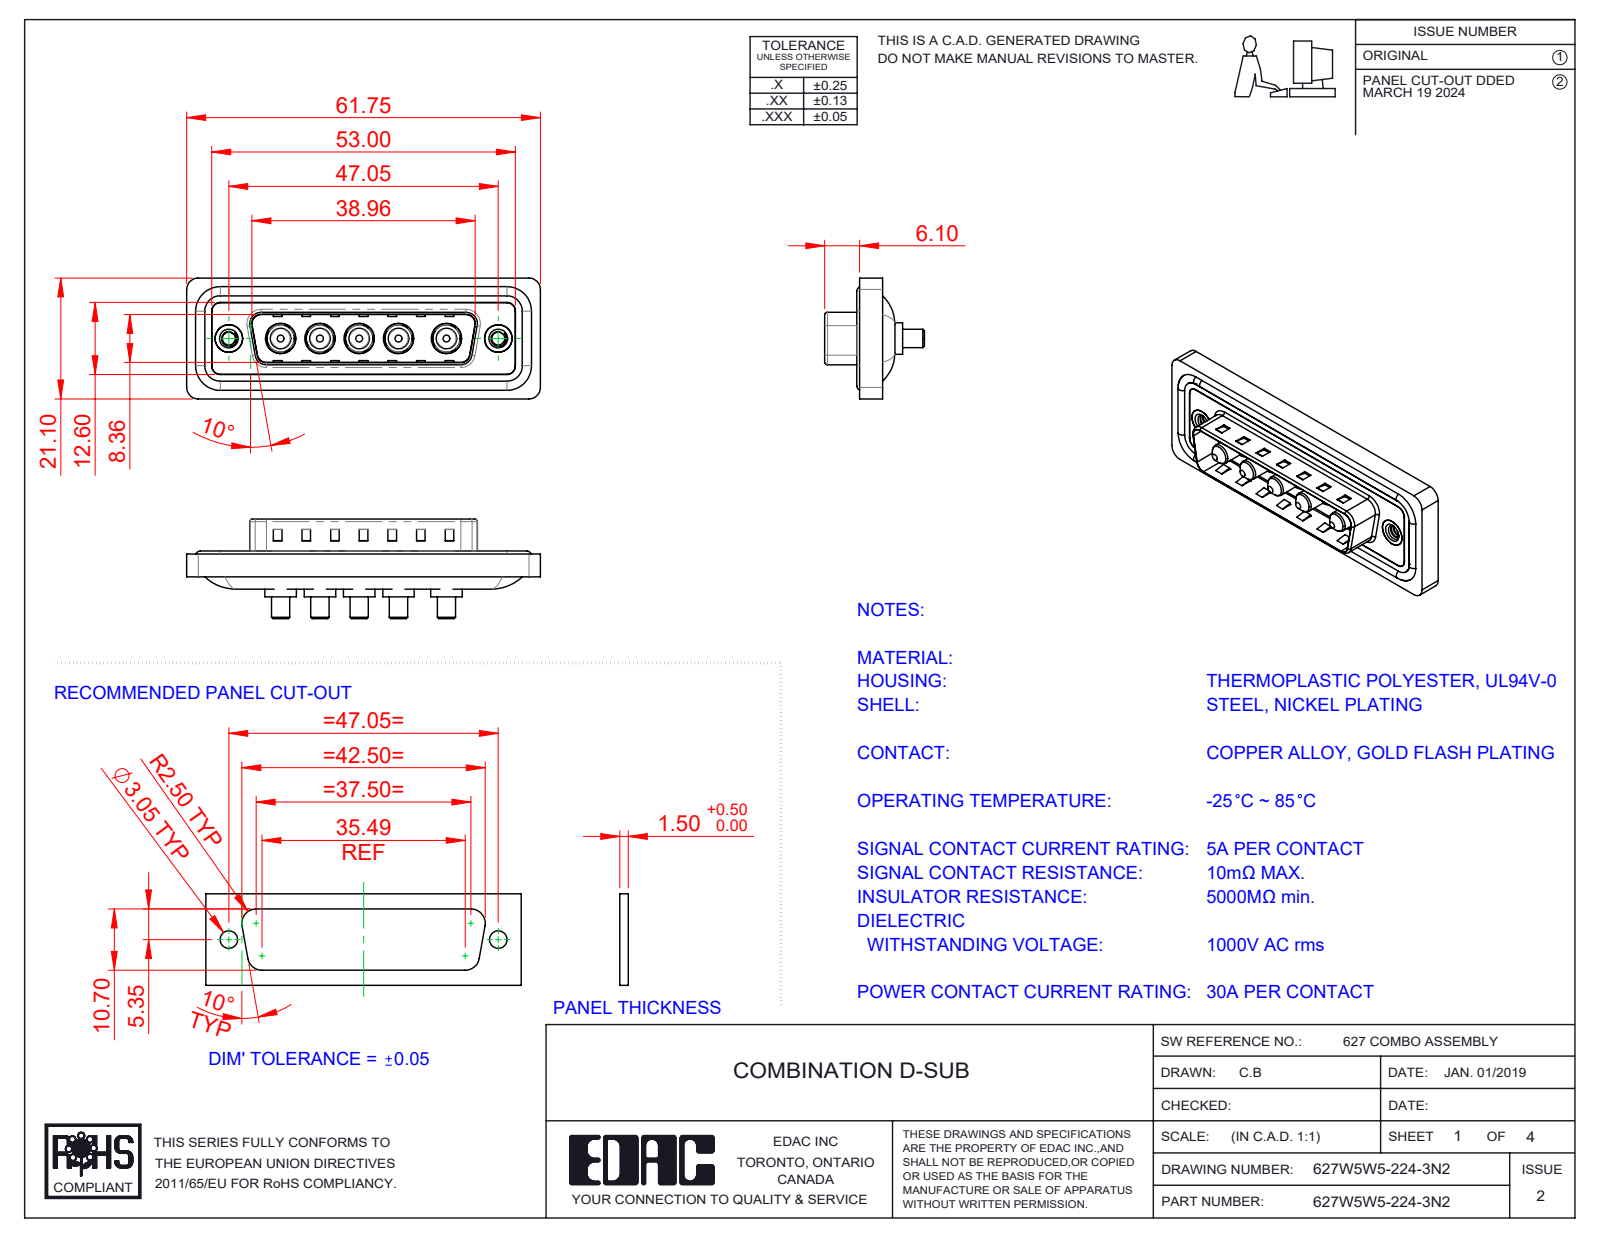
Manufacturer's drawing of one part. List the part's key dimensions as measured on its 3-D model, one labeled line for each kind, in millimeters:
Part name (STEP PRODUCT): 627Combo Waterproof Housing_25 Contacts; 627Combo Shell Rear_25 Contacts; 627Combo Threaded Rivet_2; 627Combo Housing_5W5 (+3 more)
STEP written by: SolidWorks 2023 (CONFIG_CONTROL_DESIGN)
Units: millimetres
Bodies: 17 solids, 678 faces (259 planar, 283 cylindrical, 136 other)
Overall size (bounding box): 61.75 × 21.1 × 17.4
Volume: 7 508 mm³ · Surface area: 11 819 mm²
Round holes (diameter × count): ⌀4.85 ×5, ⌀5.3 ×5, ⌀2.26 ×2, ⌀4 ×2, ⌀4.8 ×2, ⌀5 ×2
Round bosses / shafts (diameter × count): ⌀5.5 ×5, ⌀5.2 ×5, ⌀4.75 ×5, ⌀3.75 ×5, ⌀3.6 ×5, ⌀3.2 ×5, ⌀1.6 ×4, ⌀4.9 ×2
Partial cylindrical surfaces — rounded edges, fillets, slot ends (radius × count): R1.5 ×22, R2 ×18, R0.5 ×8, R1.6 ×8, R2.1 ×5, R0.25 ×4, R0.6 ×4, R0.65 ×4
Main face-to-face distances: 0.4, 1.5, 0.5, 1.1, 3.1, 1.6, 2.9, 0.82, 9.58, 5.65
Hole centre spacings: 6.86, 9.04, 13.73, 38.01, 6.87, 8.37, 8.38, 9.05
